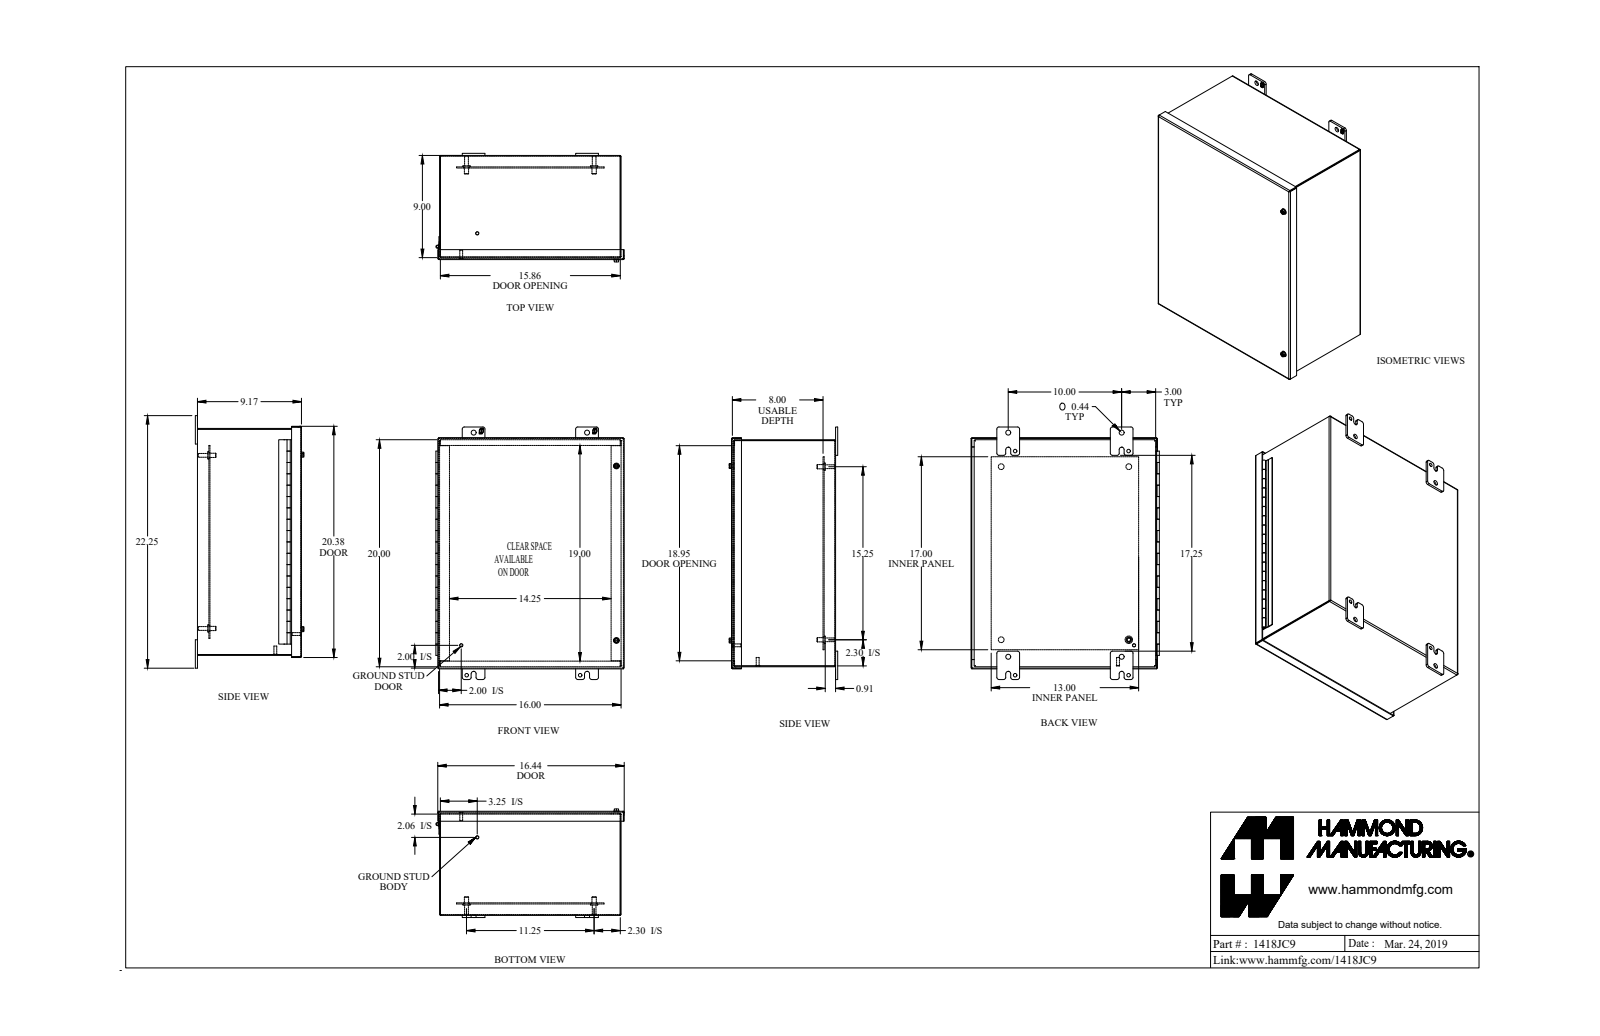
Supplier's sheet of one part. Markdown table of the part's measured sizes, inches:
| quantity | value |
| --- | --- |
| part name | 1418JC9 |
| STEP written by | SolidWorks 2019 (AUTOMOTIVE_DESIGN) |
| units | inches |
| bodies | 32 solids, 785 faces (563 planar, 198 cylindrical, 24 other) |
| overall size | 22.25 × 16.604 × 9.571 |
| volume | 148.1 in³ |
| surface area | 3 660 in² |
| round holes (diameter × count) | 0.313 × 6, 0.437 × 4, 0.5 × 4, 0.26 × 2, 0.266 × 2, 0.28 × 2, 0.29 × 2, 0.307 × 2, 0.397 × 2, 0.445 × 2, 0.187 × 1, 3.5 × 1 |
| round bosses / shafts (diameter × count) | 0.65 × 4, 0.375 × 4, 0.33 × 4, 1 × 2, 0.51 × 2, 0.5 × 2, 0.39 × 2, 0.281 × 2 |
| partial cylindrical surfaces (radius × count) | 0.188 × 24, 0.25 × 20, 0.036 × 12, 0.108 × 12, 0.218 × 8, 0.133 × 6, 0.06 × 5, 0.5 × 4 |
| main face-to-face distances | 0.072, 9.1, 15.928, 9.172, 9.028, 19.928, 8.091, 1.104, 1.032, 7.996 |
| hole center spacings | 9.475, 18.951, 1.736, 10, 11.25, 19.75, 22.137, 1.907 |
